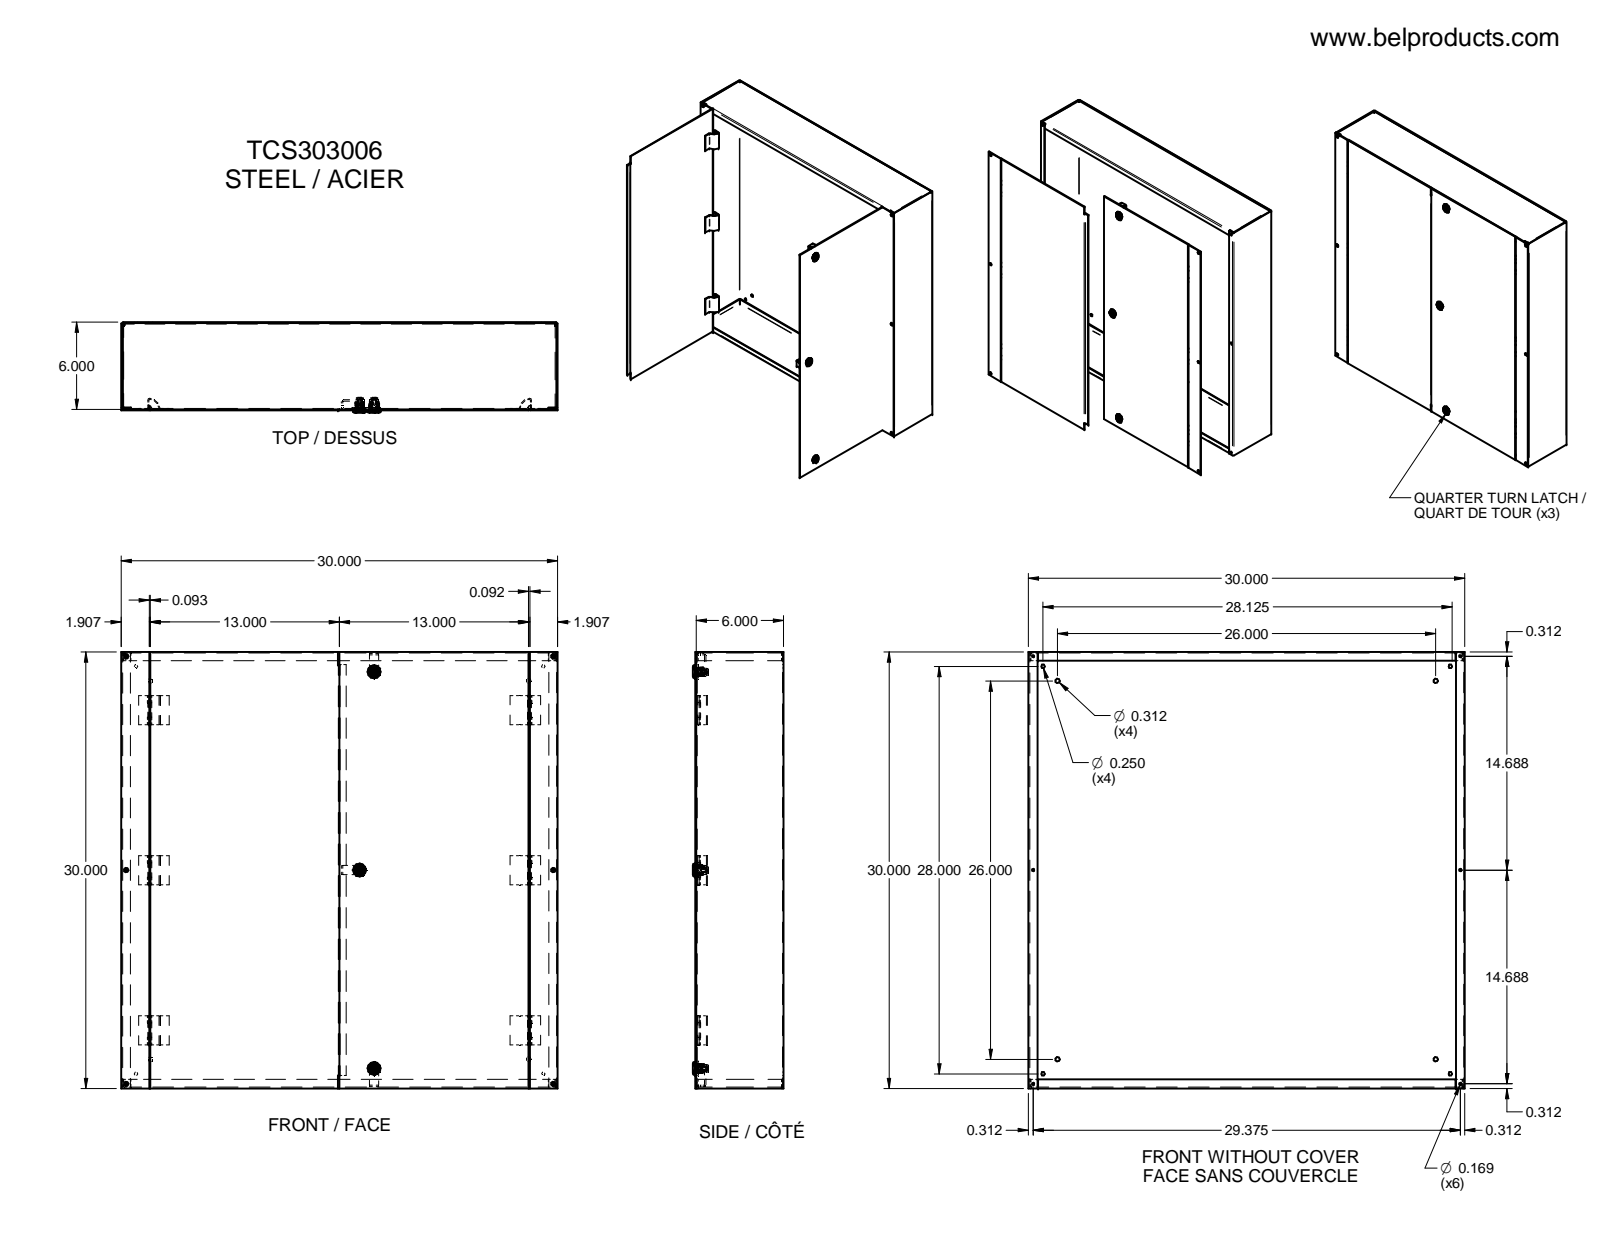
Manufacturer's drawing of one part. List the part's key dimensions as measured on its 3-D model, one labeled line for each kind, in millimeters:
Part name (STEP PRODUCT): LOCK AVEC TOURNEVIS TYPE 4-12 SANS CAME; HOSING-oa0; INSERT POUR TOURNEVIS-oa1; NOIX DE FIXATION-oa2 (+8 more)
STEP written by: Unknown (AUTOMOTIVE_DESIGN)
Units: millimetres
Bodies: 46 solids, 1689 faces (850 planar, 417 cylindrical, 422 other)
Overall size (bounding box): 762 × 762 × 158.78
Volume: 3 283 000 mm³ · Surface area: 3 492 000 mm²
Round holes (diameter × count): ⌀7.92 ×10, ⌀4.29 ×6, ⌀6.35 ×4, ⌀9.1 ×3, ⌀11.18 ×3, ⌀12.83 ×3, ⌀15.8 ×3, ⌀17.46 ×3, ⌀3.81 ×2, ⌀6.99 ×2
Round bosses / shafts (diameter × count): ⌀22.86 ×3, ⌀22.61 ×3, ⌀15.75 ×3, ⌀12.95 ×3, ⌀12.62 ×3, ⌀12.19 ×3, ⌀11.86 ×3, ⌀10.08 ×3
Partial cylindrical surfaces — rounded edges, fillets, slot ends (radius × count): R9.53 ×34, R0.25 ×24, R0.81 ×17, R2.72 ×14, R9.42 ×6, R1.52 ×4, R3.05 ×4, R3.48 ×3
Main face-to-face distances: 1.91, 152.4, 150.49, 154.31, 1.9, 760.1, 762, 758.2, 150.5, 3.81
Hole centre spacings: 686.27, 704.56, 728.87, 746.12, 24.69, 35.92, 60.61, 332.97
